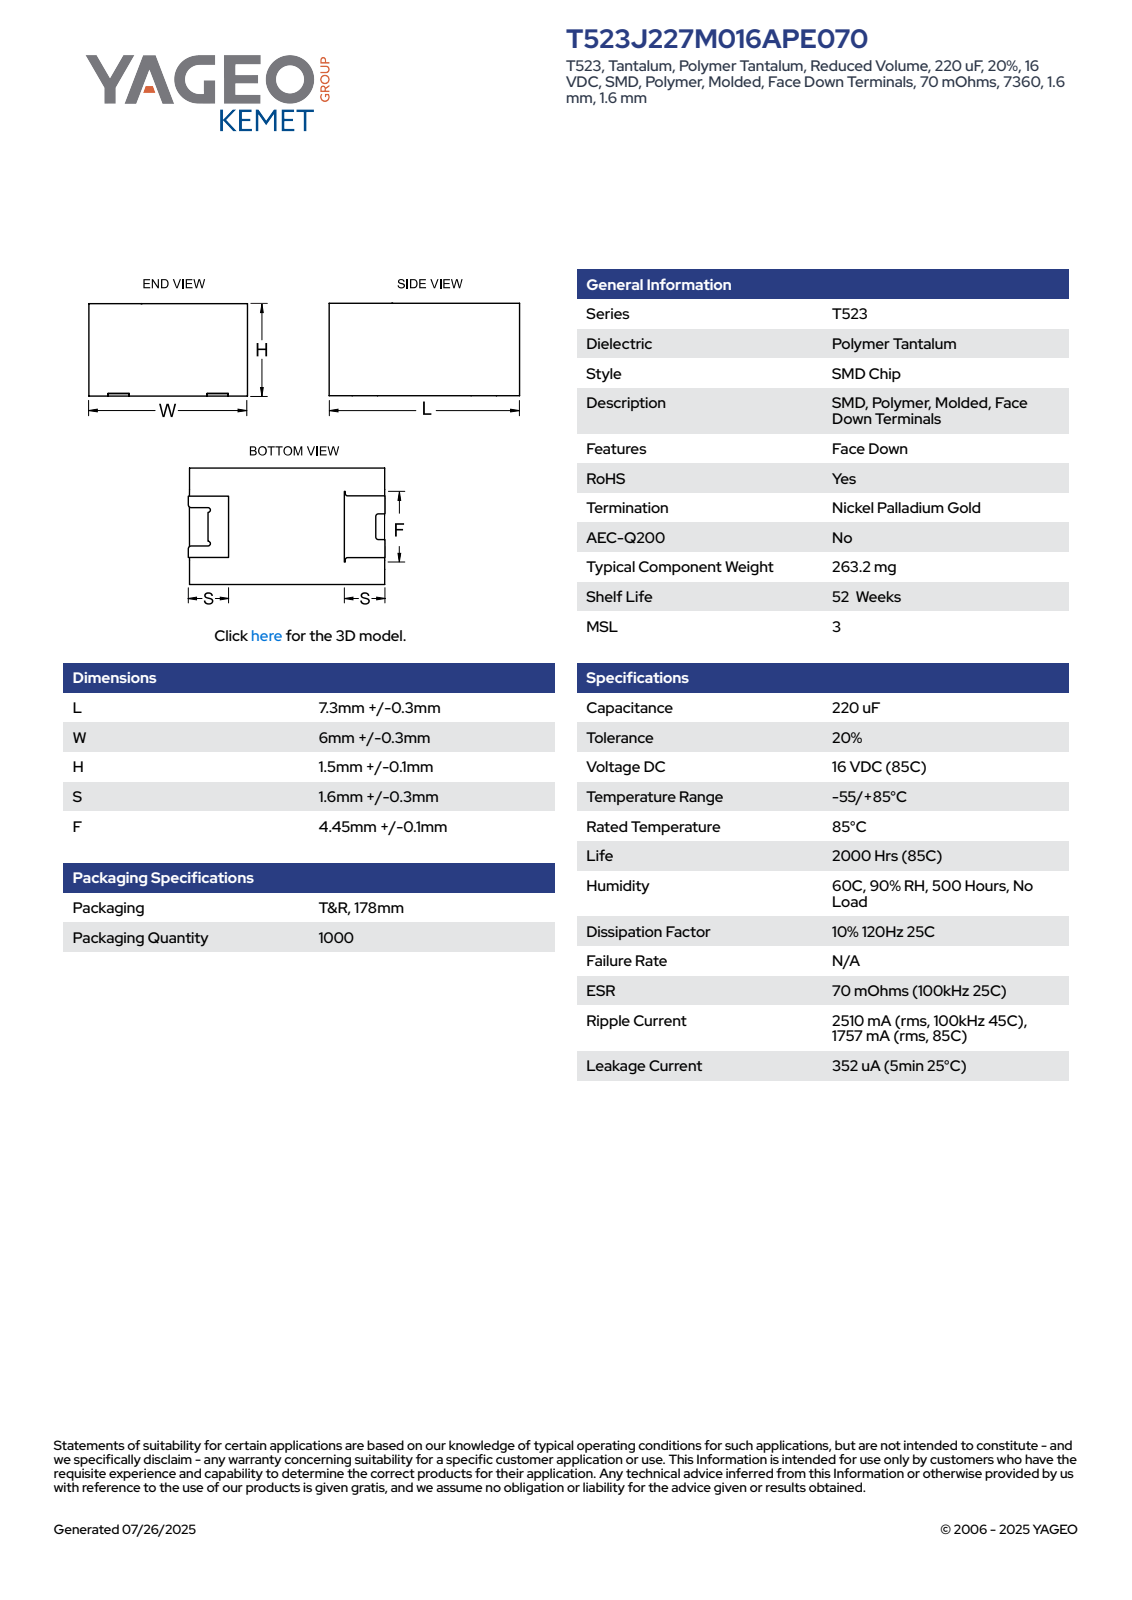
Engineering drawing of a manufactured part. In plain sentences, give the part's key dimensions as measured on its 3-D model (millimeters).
The part is named "CTS_TFD_JVW_7360_L7.6W6.3H1.6S1.6F4.55". Its 3-D file was written by "SolidWorks 2020 (AUTOMOTIVE_DESIGN)". It is 4 solids with 91 faces: 89 planar, 2 cylindrical and 0 other. Overall it measures 7.62 by 6.3 by 1.61 millimeters. Its volume is 77 cubic millimeters and its surface area 147 square millimeters. Partial cylindrical surfaces (rounded edges, fillets, slot ends): 2 of radius 0.2. The main face-to-face distances are 1.6, 6.3, 1.61, 7.6, 7.61, 7.62, 6.01, 6, 4.4, 0.8.
